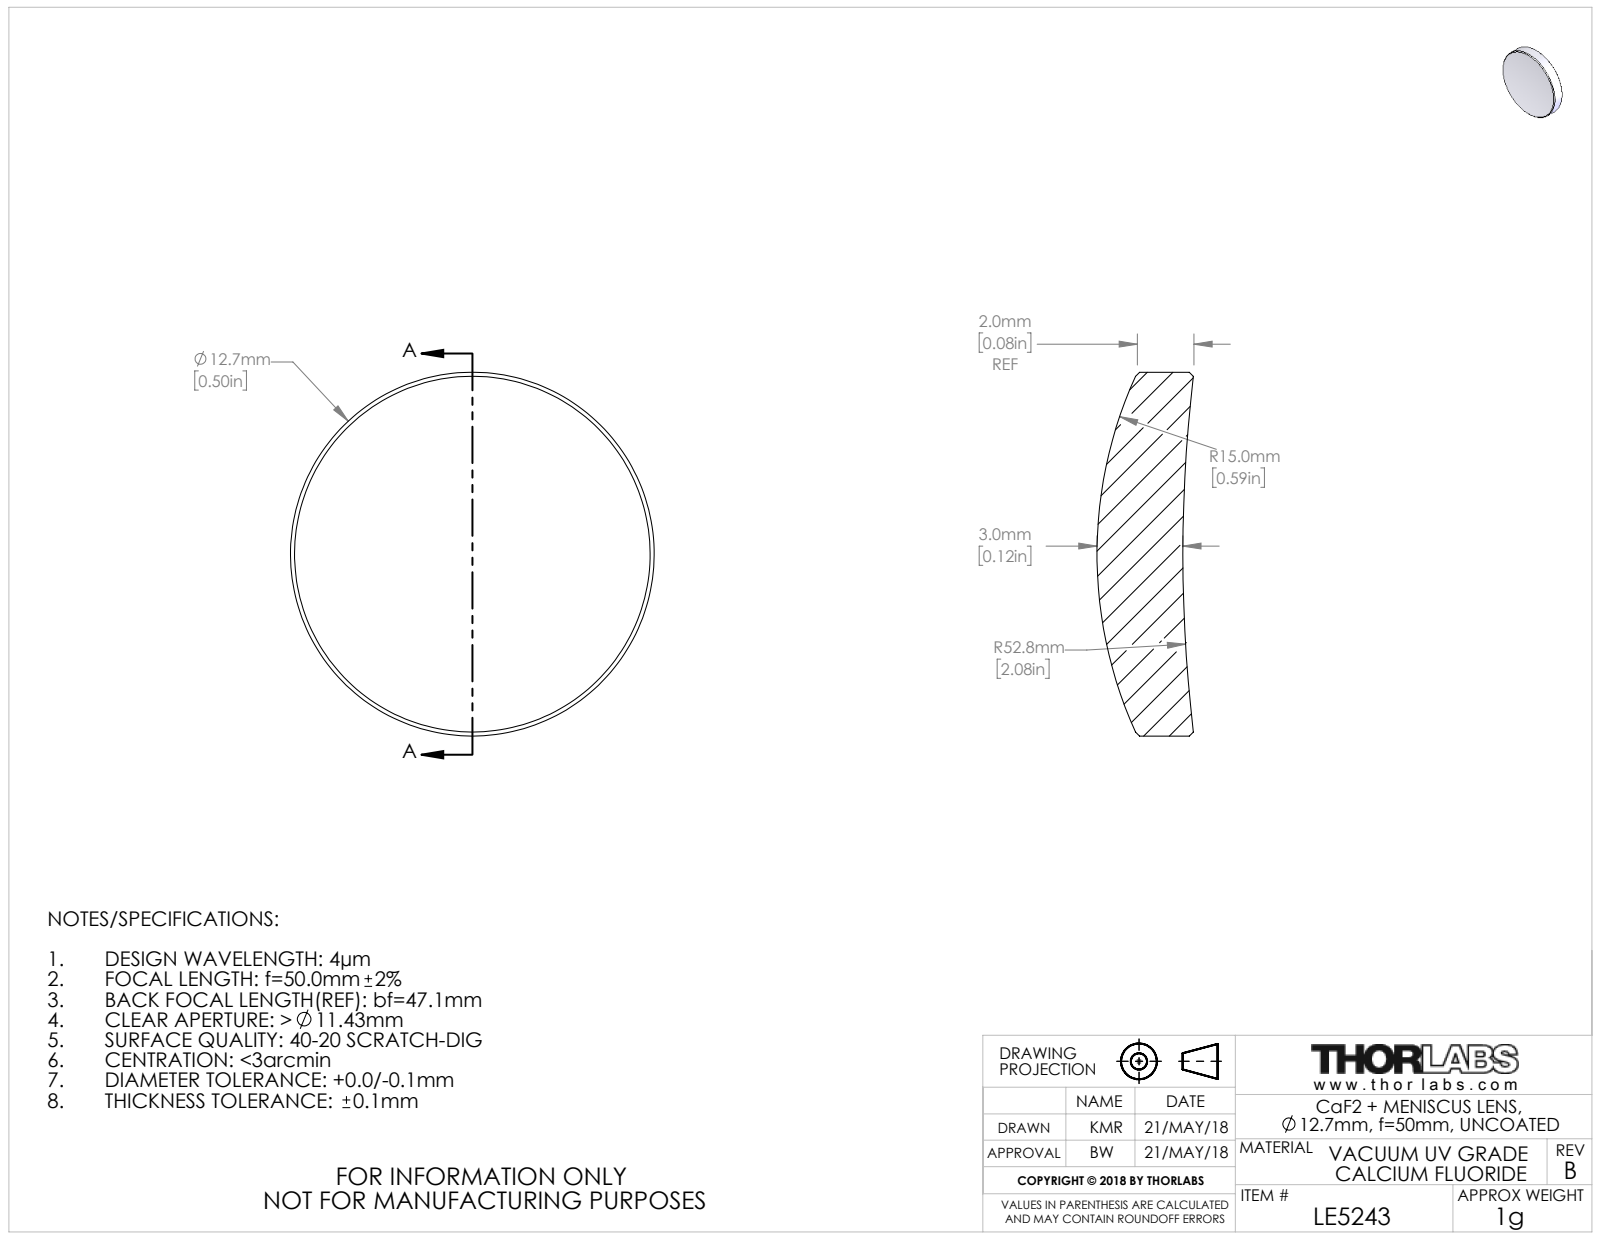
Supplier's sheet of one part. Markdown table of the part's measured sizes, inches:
| quantity | value |
| --- | --- |
| part name | 21984-E0W |
| STEP written by | SolidWorks 2016 (CONFIG_CONTROL_DESIGN) |
| units | inches |
| bodies | 1 solid, 10 faces (0 planar, 2 cylindrical, 8 other) |
| overall size | 0.5 × 0.5 × 0.133 |
| volume | 0.019 in³ |
| surface area | 0.517 in² |
| round bosses / shafts (diameter × count) | 0.5 × 1 |
